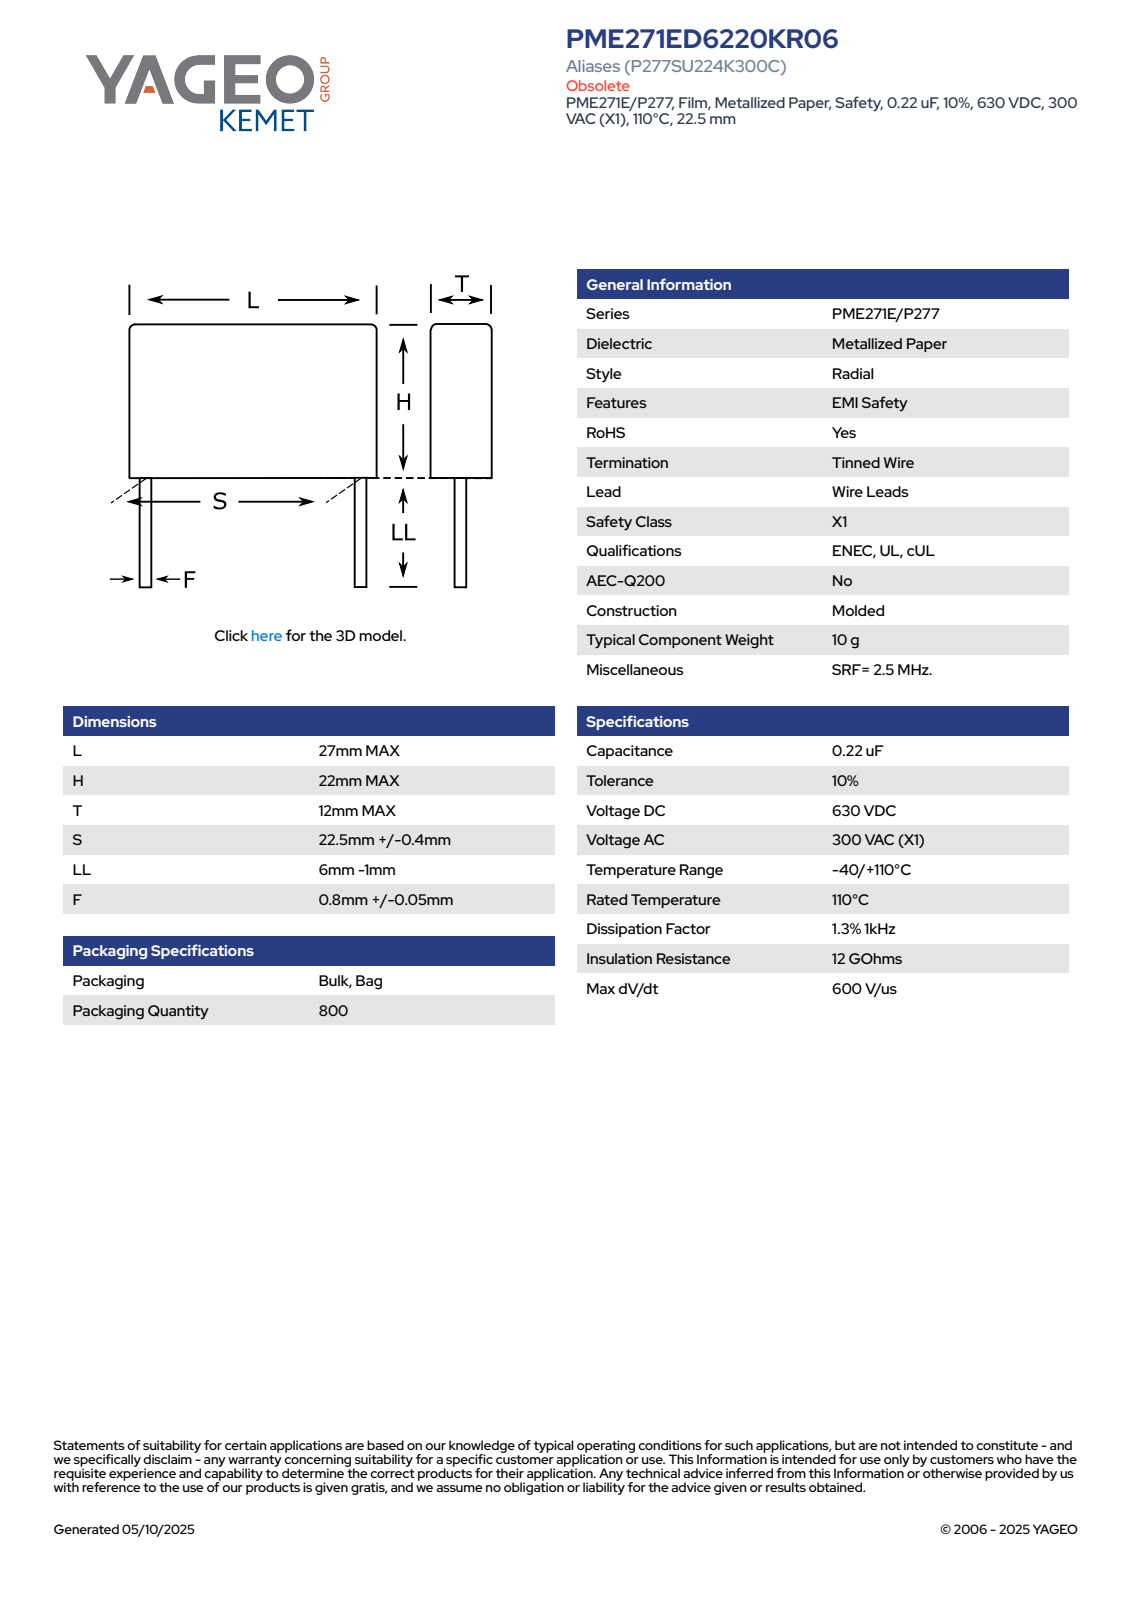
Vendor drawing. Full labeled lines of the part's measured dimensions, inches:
Part name (STEP PRODUCT): CFR_MOLDED_27X22X12_L27H22T12S22.5LL5F0.85
STEP written by: SolidWorks 2014 (AUTOMOTIVE_DESIGN)
Units: inches
Bodies: 4 solids, 73 faces (65 planar, 8 cylindrical, 0 other)
Overall size (bounding box): 1.063 × 1.063 × 0.473
Volume: 0.435 in³ · Surface area: 3.734 in²
Round bosses / shafts (diameter × count): ⌀0.033 ×2
Partial cylindrical surfaces — rounded edges, fillets, slot ends (radius × count): R0.02 ×4
Main face-to-face distances: 0.472, 0.866, 1.063, 0.473, 0.197, 0.655, 0.458, 0.408, 0.56, 0.363
